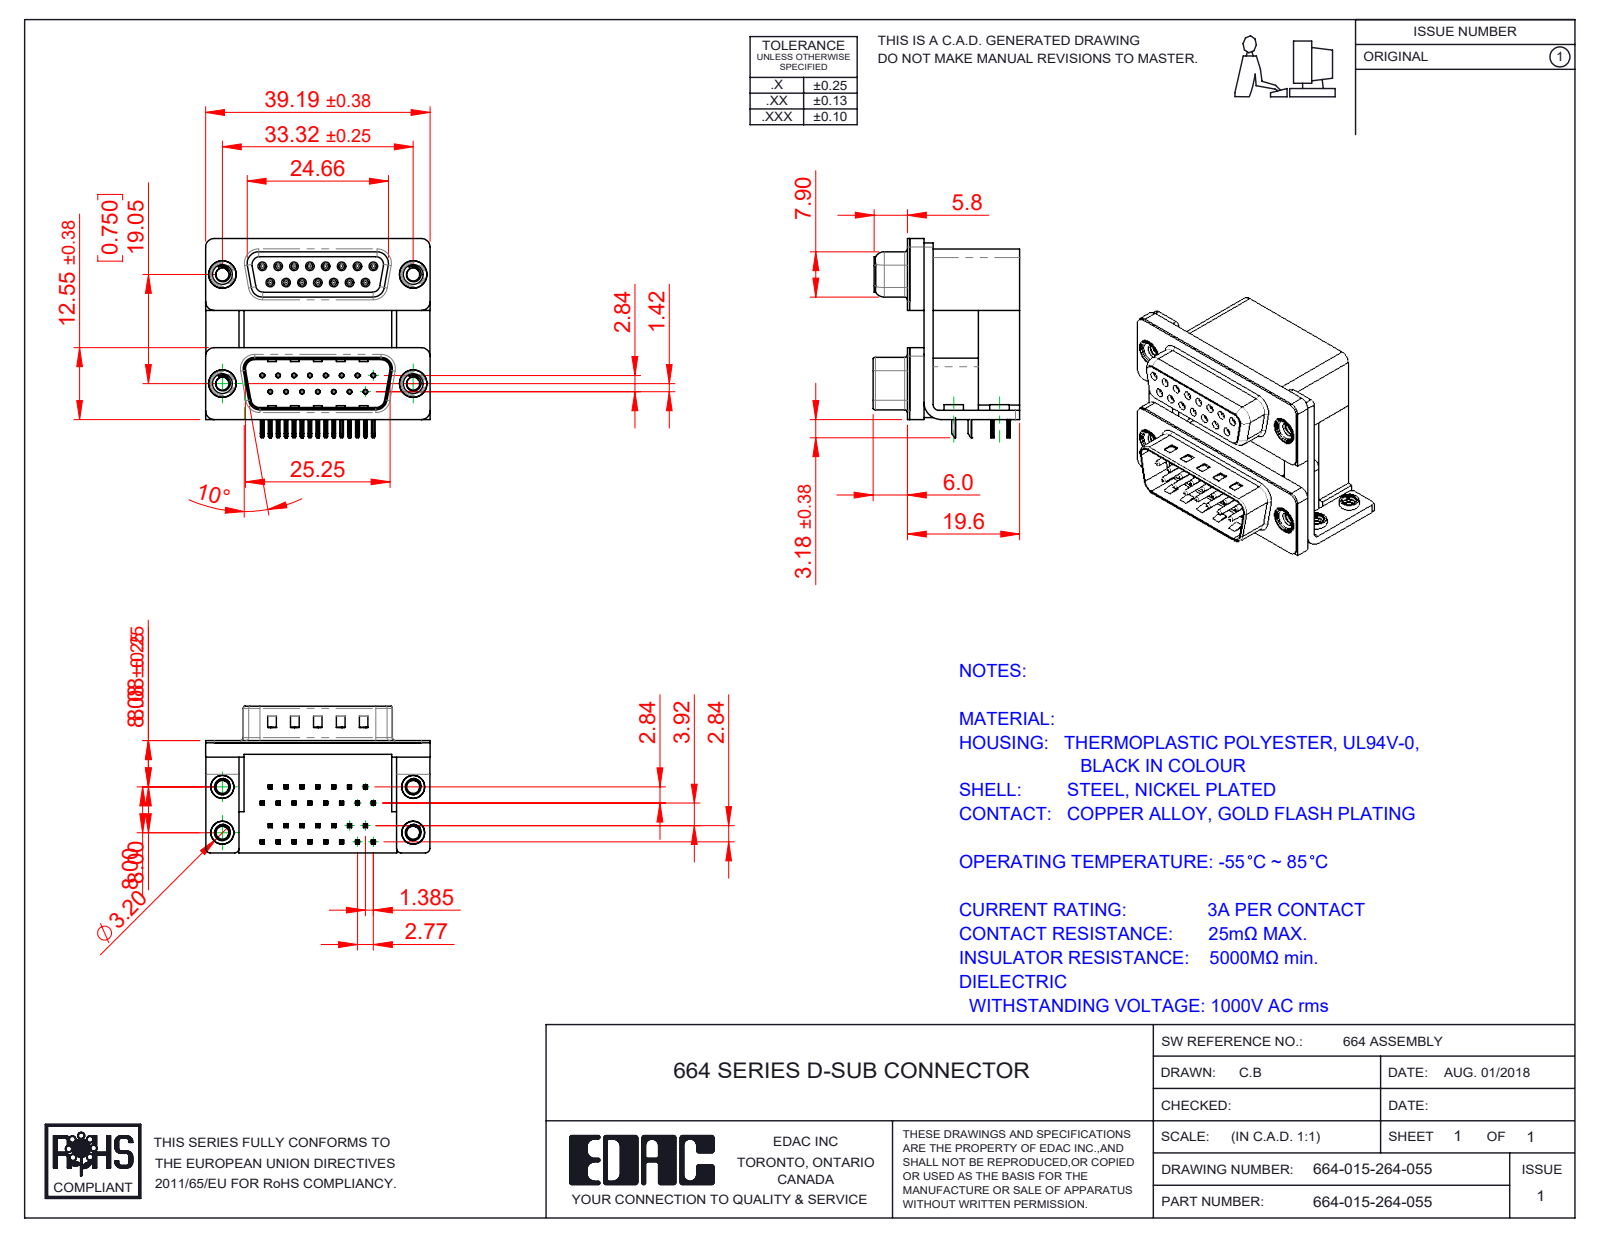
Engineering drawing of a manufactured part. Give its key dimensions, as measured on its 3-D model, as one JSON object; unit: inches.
{"part_name": "664 Housing Lower_15 Contacts; 664 Contact Top Lower; 664 Housing Spacer_15 Contacts M; 664 Contact Bottom Upper_M (+8 more)", "step_written_by": "SolidWorks 2020 (CONFIG_CONTROL_DESIGN)", "units": "inches", "bodies": {"solids": 45, "faces": 4052, "planar": 2027, "cylindrical": 1090, "other": 935}, "overall_size": [1.543, 1.369, 1.008], "volume_in3": 0.928, "surface_area_in2": 26.51, "round_holes": [[0.031, 30], [0.014, 15], [0.035, 15], [0.089, 8], [0.108, 4], [0.126, 4], [0.138, 4], [0.157, 4], [0.189, 4], [0.197, 4]], "round_bosses_or_shafts": [[0.047, 15], [0.03, 15], [0.193, 4], [0.187, 4], [0.157, 4], [0.154, 4], [0.134, 4]], "partial_cylinders_radius": [[0.004, 120], [0.006, 60], [0.01, 60], [0.005, 30], [0.014, 30], [0.059, 16], [0.013, 15], [0.02, 12]], "face_to_face_distances": [0.016, 0.756, 0.657, 0.098, 0.283, 0.472, 0.374, 0.421, 0.086, 0.114], "hole_center_spacings": [0.124, 0.109, 0.758, 0.218, 0.781, 0.327, 0.75, 0.818]}
